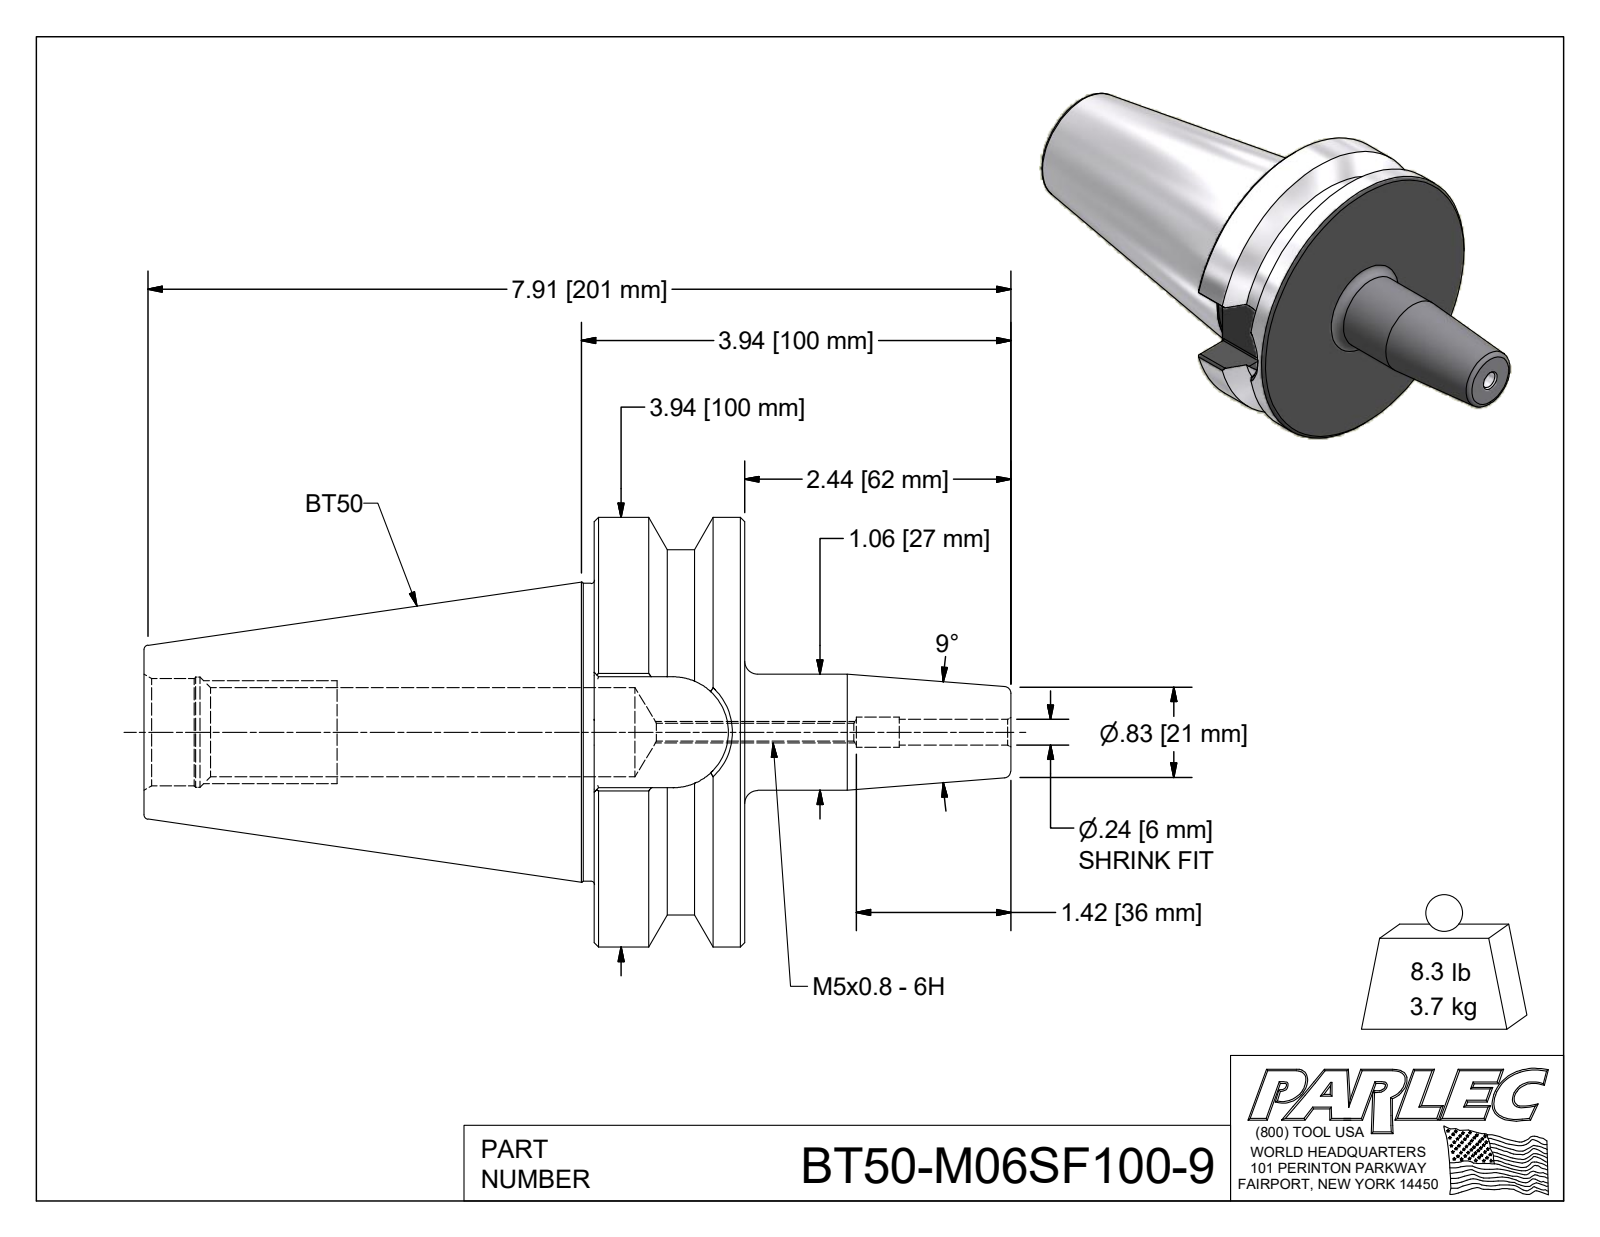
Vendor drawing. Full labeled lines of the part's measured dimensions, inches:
Part name (STEP PRODUCT): BT50-M06SF100-9; BT50BC-M06SF100-9-1; 029-966; BS-SFM058-16
STEP written by: Autodesk Inventor 2009 (AUTOMOTIVE_DESIGN)
Units: inches
Bodies: 6 solids, 172 faces (79 planar, 42 cylindrical, 51 other)
Overall size (bounding box): 7.945 × 3.937 × 3.937
Volume: 28.98 in³ · Surface area: 95.9 in²
Round holes (diameter × count): ⌀0.197 ×4, ⌀0.24 ×4, ⌀0.236 ×1, ⌀0.266 ×1, ⌀1.009 ×1
Round bosses / shafts (diameter × count): ⌀0.244 ×4, ⌀0.236 ×4, ⌀3.937 ×1, ⌀3.346 ×1, ⌀2.73 ×1, ⌀1.063 ×1
Partial cylindrical surfaces — rounded edges, fillets, slot ends (radius × count): R0.02 ×8, R0.098 ×1, R0.508 ×1
Main face-to-face distances: 1.378, 2.788, 4.126, 5.504, 1.016, 7.945, 3.819, 2.441, 5.058, 0.932
